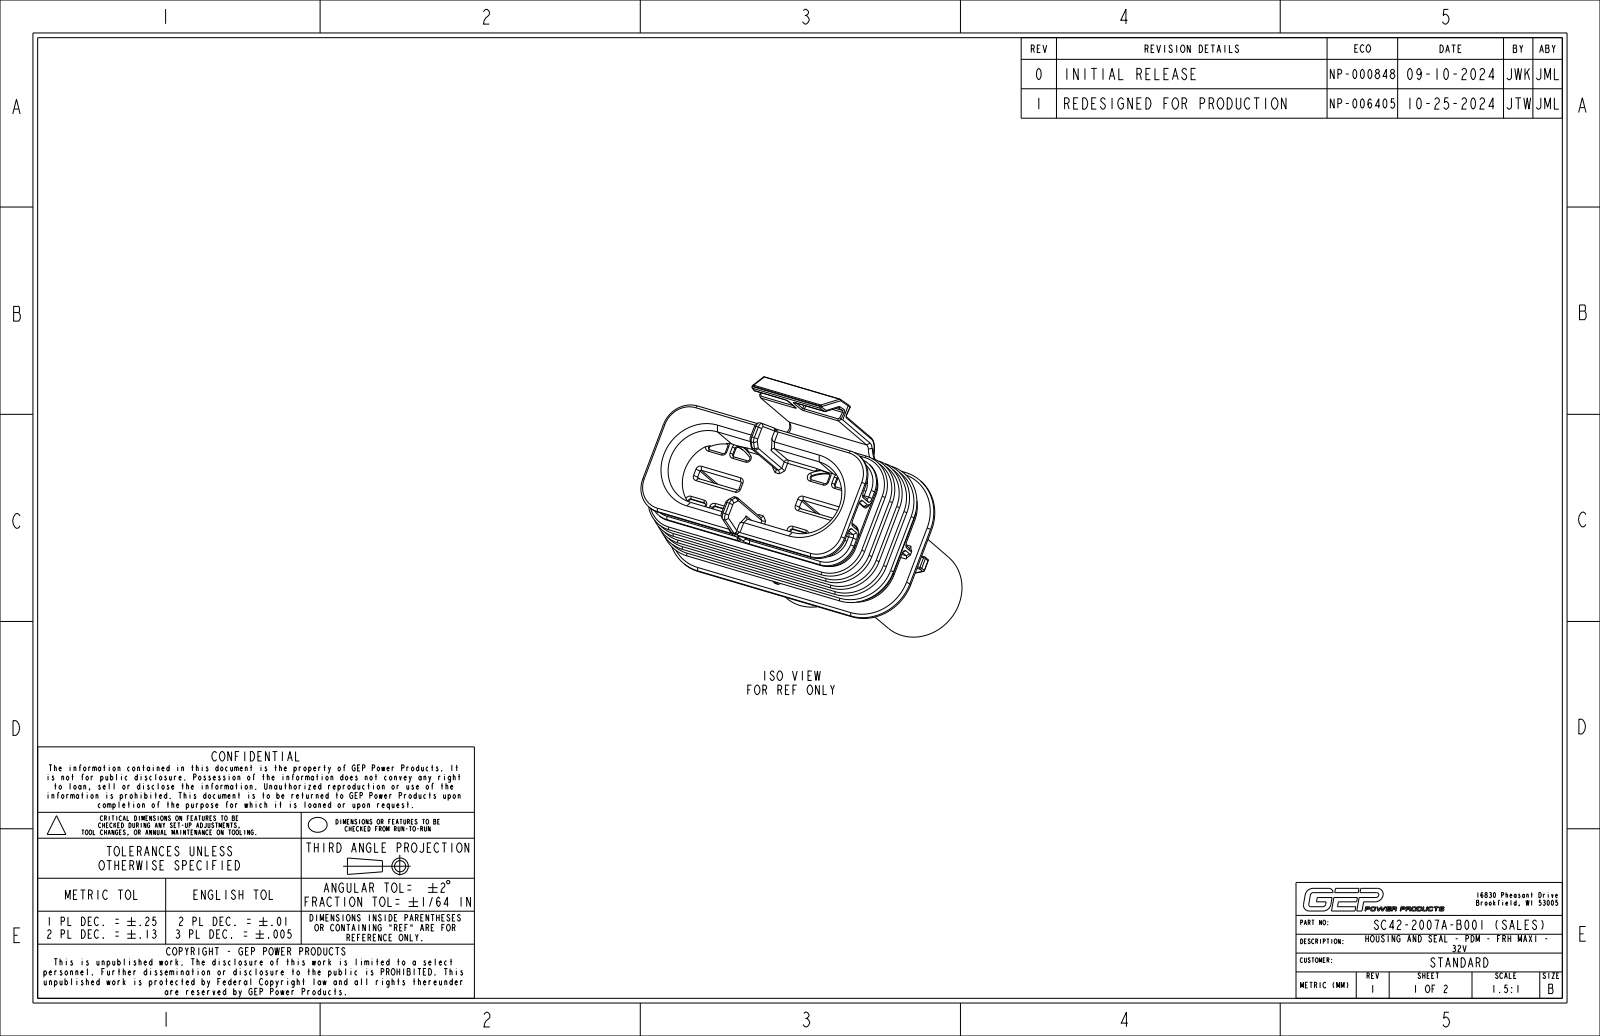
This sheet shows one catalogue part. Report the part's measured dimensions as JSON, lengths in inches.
{"part_name": "PC26-2001A-B001_SALES_NCF; PC14-2001A-B015_INST; PC42-2007A-B001_SALES_NCF_ASM; SC42-2007A-B001_NCF_ASM", "step_written_by": "CREO PARAMETRIC BY PTC INC, 2024014 (CONFIG_CONTROL_DESIGN)", "units": "inches", "bodies": {"solids": 2, "faces": 1331, "planar": 470, "cylindrical": 409, "other": 452}, "overall_size": [2.626, 1.929, 1.331], "volume_in3": 1.629, "surface_area_in2": 34.57, "round_bosses_or_shafts": [[0.118, 1]], "partial_cylinders_radius": [[0.02, 106], [0.01, 59], [0.016, 44], [0.012, 40], [0.008, 8], [0.039, 8], [0.138, 4], [0.177, 4]], "face_to_face_distances": [0.059, 0.11, 0.298, 0.361, 0.22, 0.66, 0.079, 0.177, 0.031, 0.472]}
